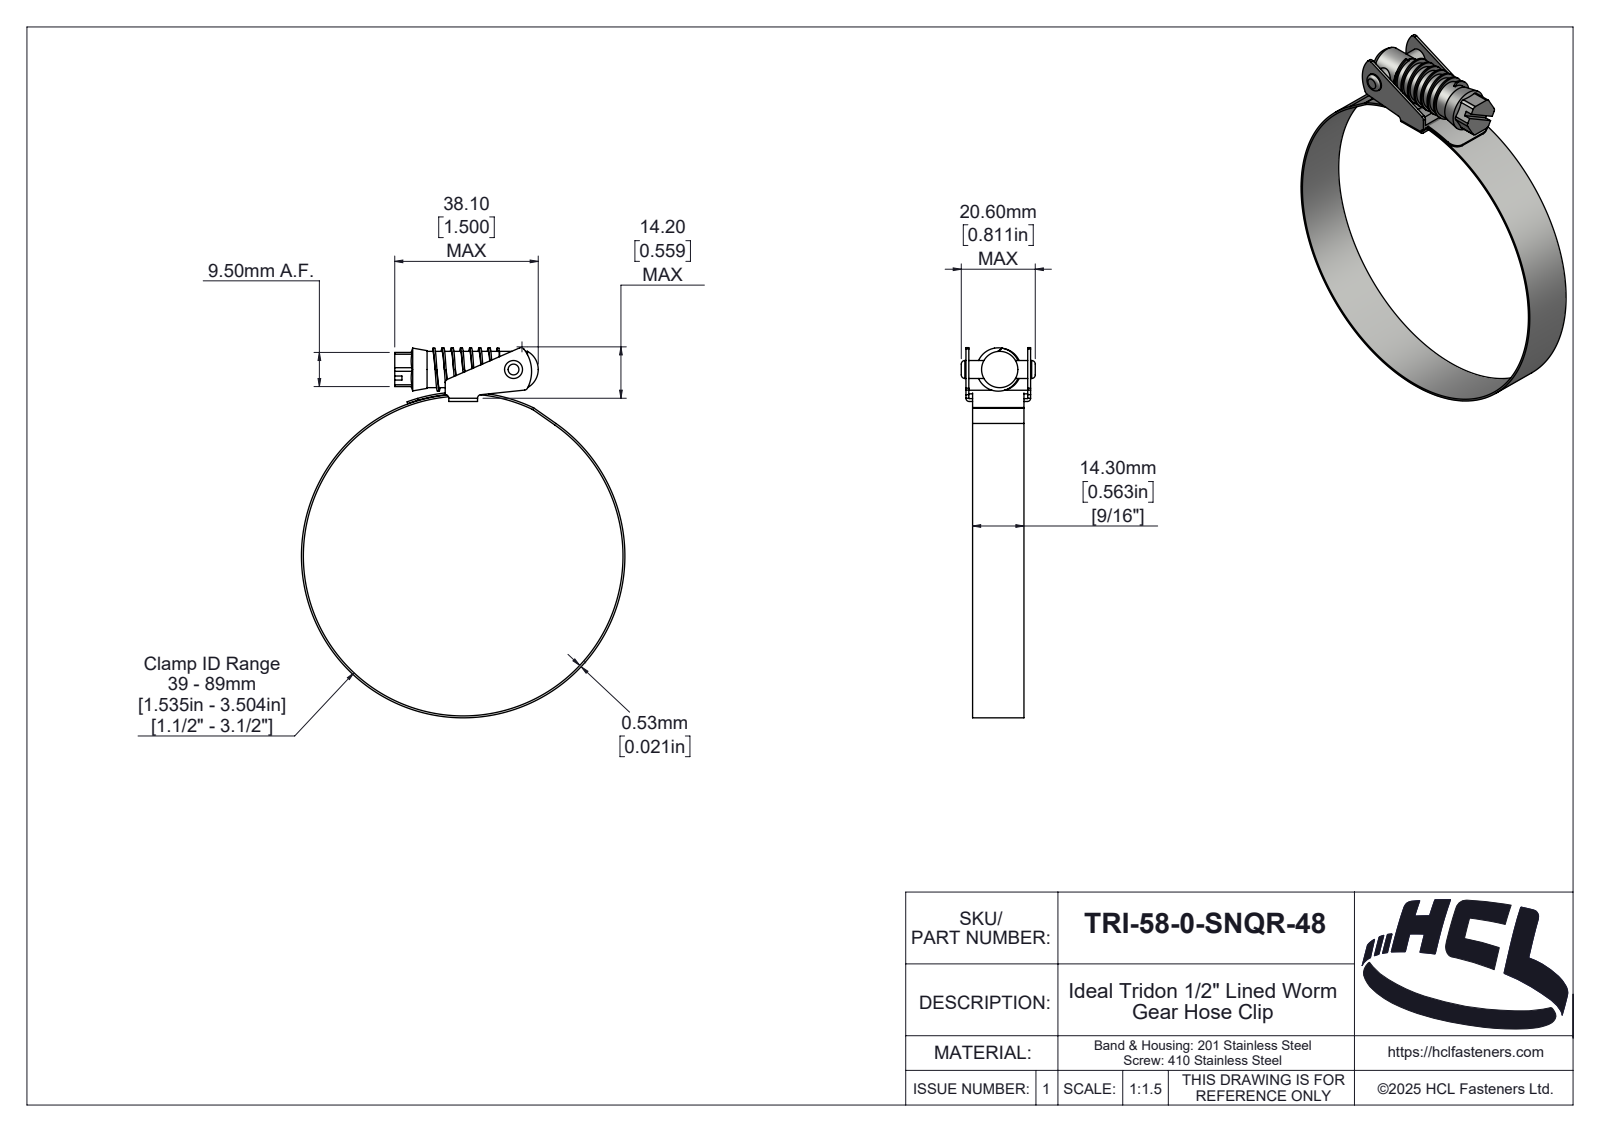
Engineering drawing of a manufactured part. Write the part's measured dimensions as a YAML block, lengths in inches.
part_name: "TRI-58-0-SNQR-48"
step_written_by: "SolidWorks 2025 (AUTOMOTIVE_DESIGN)"
units: inches
bodies: {solids: 5, faces: 222, planar: 44, cylindrical: 112, other: 66}
overall_size: [4.056, 3.546, 0.811]
volume: 0.371
surface_area: 19.79
round_holes:
  - {diameter: 0.197, count: 1}
  - {diameter: 3.504, count: 1}
round_bosses_or_shafts:
  - {diameter: 3.546, count: 1}
  - {diameter: 0.398, count: 1}
partial_cylinders:
  - {radius: 0.039, count: 11}
  - {radius: 0.004, count: 2}
  - {radius: 0.035, count: 2}
  - {radius: 0.118, count: 2}
  - {radius: 0.018, count: 1}
  - {radius: 0.074, count: 1}
  - {radius: 0.079, count: 1}
  - {radius: 0.093, count: 1}
face_to_face_distances: [0.031, 0.677, 0.073, 0.636, 0.041, 0.604, 0.709, 0.646, 0.563, 0.039]
hole_center_spacings: [2.117]
